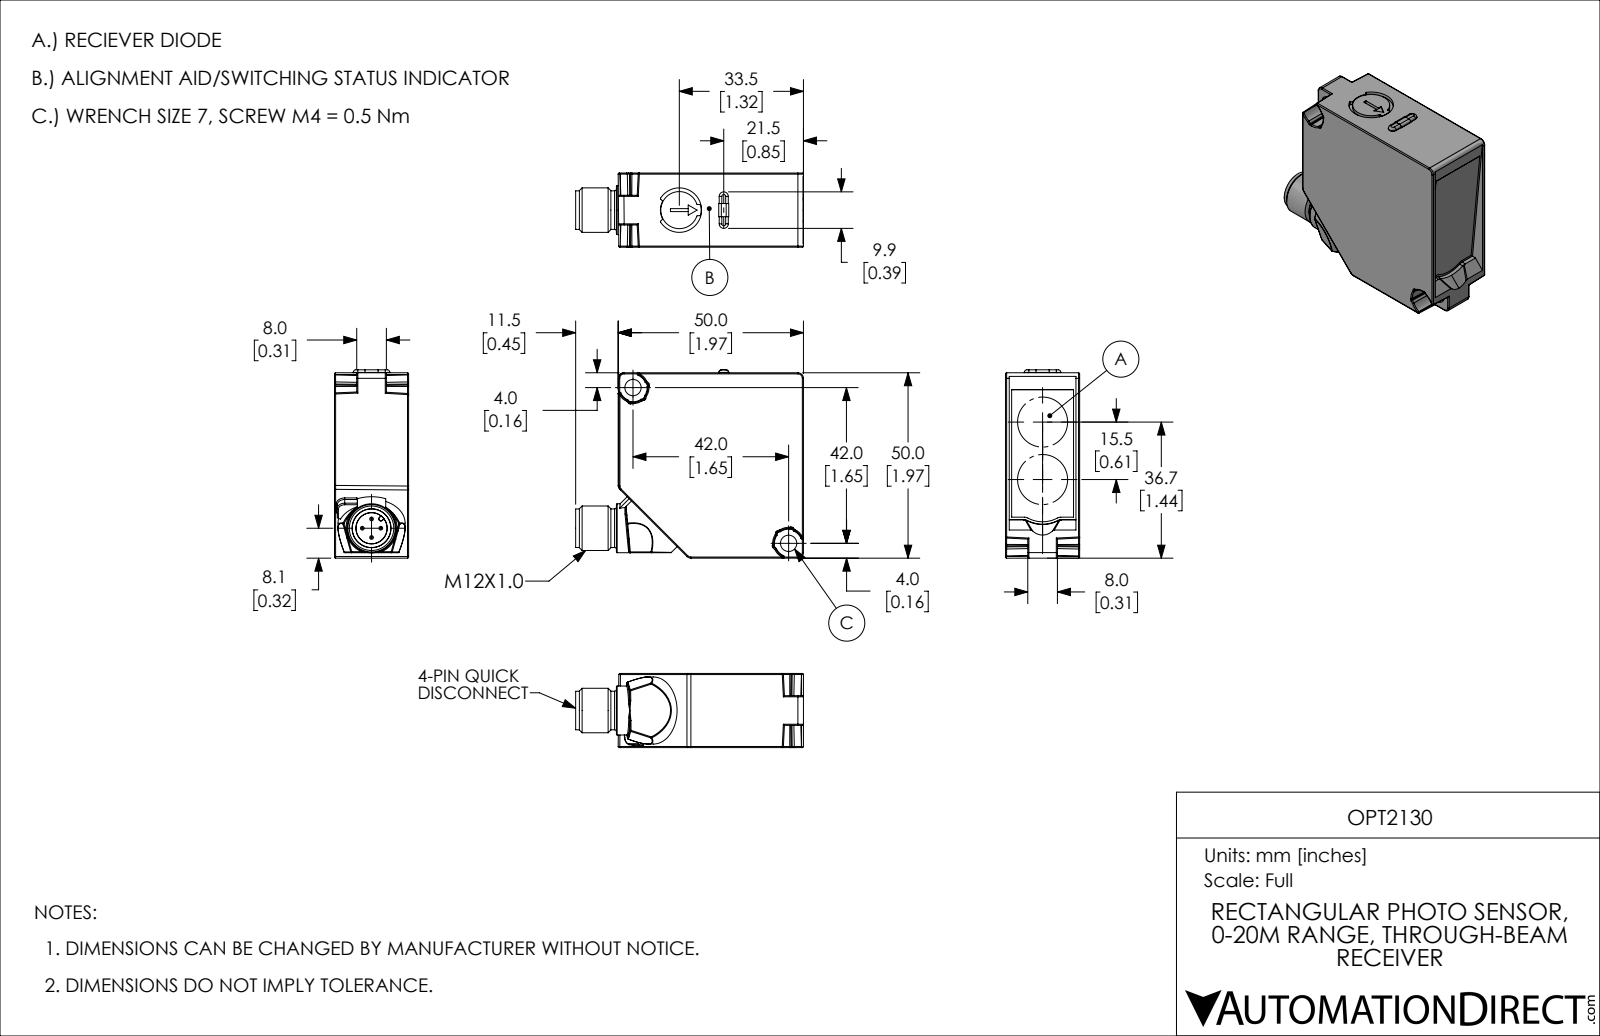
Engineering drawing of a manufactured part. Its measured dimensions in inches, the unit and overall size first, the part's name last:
Units: inches
Overall size (bounding box): 2.42 × 2 × 0.787
Round holes (diameter × count): ⌀0.173 ×2, ⌀0.472 ×1, ⌀0.713 ×1
Round bosses / shafts (diameter × count): ⌀0.039 ×4, ⌀0.52 ×1, ⌀0.472 ×1, ⌀0.409 ×1, ⌀0.394 ×1
Partial cylindrical surfaces — rounded edges, fillets, slot ends (radius × count): R0.012 ×63, R0.008 ×8, R0.059 ×5, R0.079 ×5, R0.028 ×4, R0.048 ×2, R0.201 ×1, R0.232 ×1
Main face-to-face distances: 0.787, 1.969, 0.039, 0.748, 0.236, 0.551, 0.197, 0.512, 0.058, 1.911
Hole centre spacings: 2.339
Volume: 2.816 in³ · Surface area: 16.5 in²
Bodies: 2 solids, 342 faces (110 planar, 119 cylindrical, 113 other)
Part name (STEP PRODUCT): OPT2130
STEP written by: SolidWorks 2019 (AUTOMOTIVE_DESIGN)
